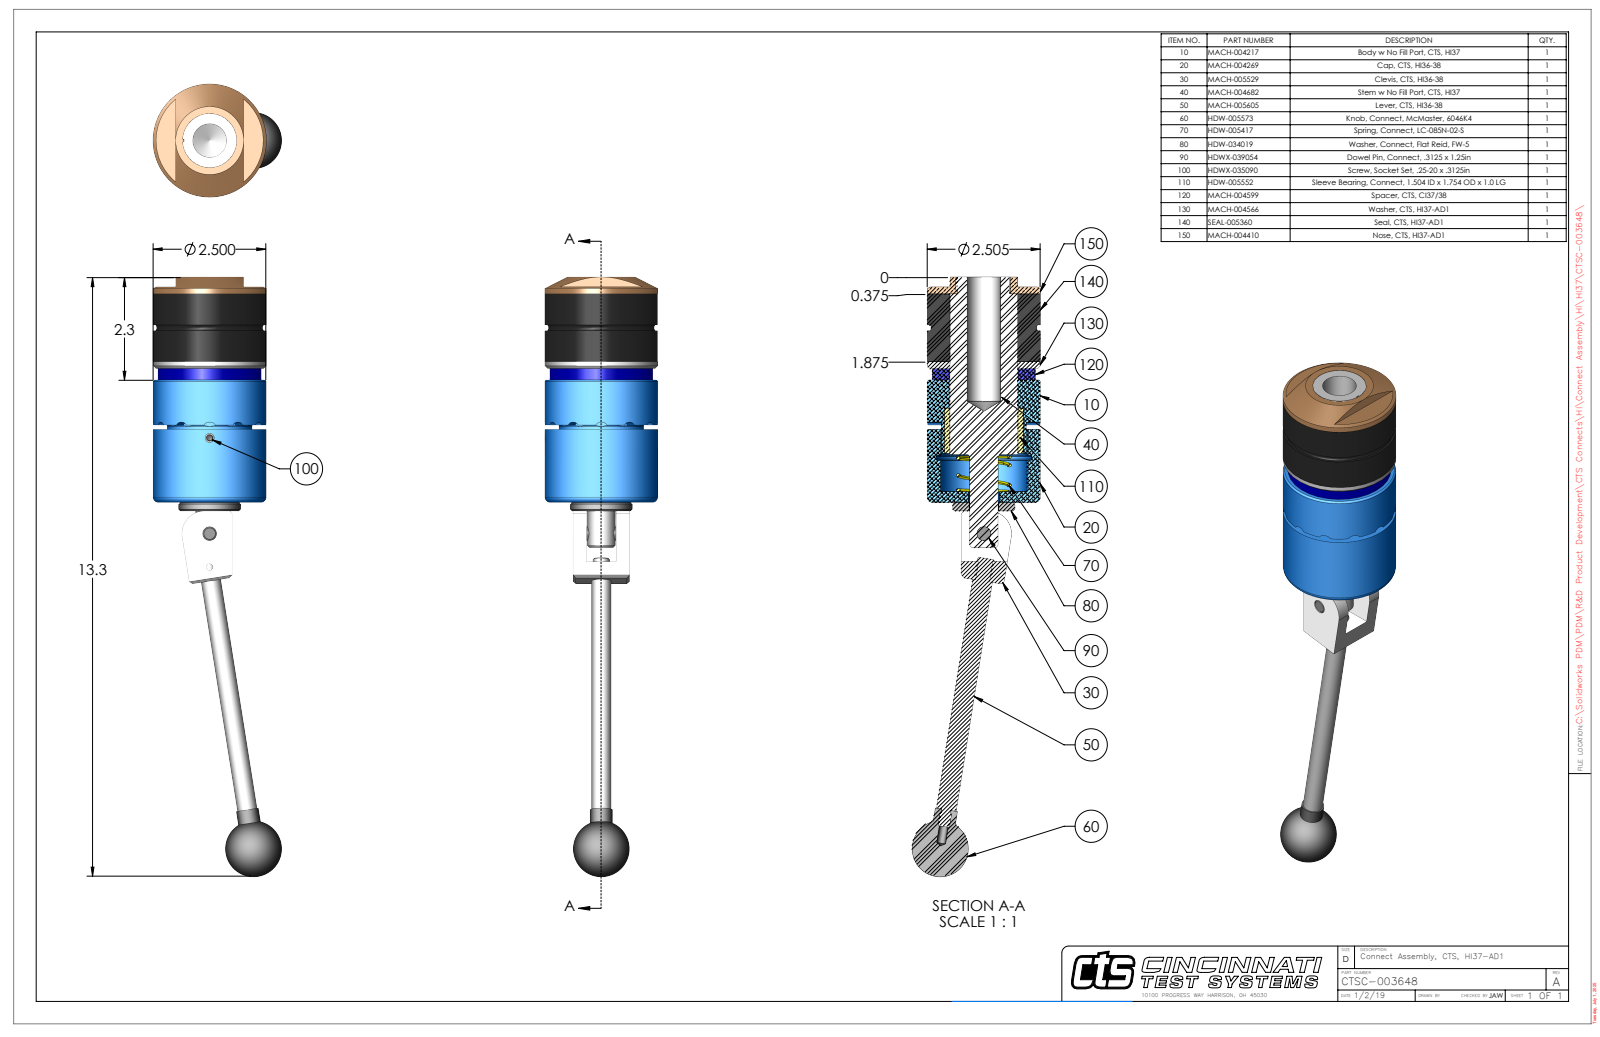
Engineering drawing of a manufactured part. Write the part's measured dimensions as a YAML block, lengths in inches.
part_name: "CTSC-003648"
step_written_by: "SolidWorks 2023 (AUTOMOTIVE_DESIGN)"
units: inches
bodies: {solids: 11, faces: 279, planar: 97, cylindrical: 110, other: 72}
overall_size: [13.275, 2.845, 2.505]
volume: 25.9
surface_area: 139.7
round_holes:
  - {diameter: 0.201, count: 2}
  - {diameter: 0.15, count: 1}
  - {diameter: 0.311, count: 1}
  - {diameter: 0.313, count: 1}
  - {diameter: 0.314, count: 1}
  - {diameter: 0.656, count: 1}
  - {diameter: 0.696, count: 1}
  - {diameter: 0.75, count: 1}
  - {diameter: 1.172, count: 1}
  - {diameter: 1.495, count: 1}
  - {diameter: 1.501, count: 1}
  - {diameter: 1.51, count: 1}
round_bosses_or_shafts:
  - {diameter: 2.505, count: 1}
  - {diameter: 2.505, count: 1}
  - {diameter: 2.5, count: 1}
  - {diameter: 2.281, count: 1}
  - {diameter: 1.875, count: 1}
  - {diameter: 1.5, count: 1}
  - {diameter: 1.496, count: 1}
  - {diameter: 1.38, count: 1}
partial_cylinders:
  - {radius: 0.12, count: 12}
  - {radius: 0.029, count: 2}
  - {radius: 0.5, count: 1}
  - {radius: 1.206, count: 1}
face_to_face_distances: [1.5, 0.25, 0.402, 1.902, 0.152, 1.652, 2.713, 2.963, 3.115, 4.615]
hole_center_spacings: [0.74, 2.118, 2.858]
